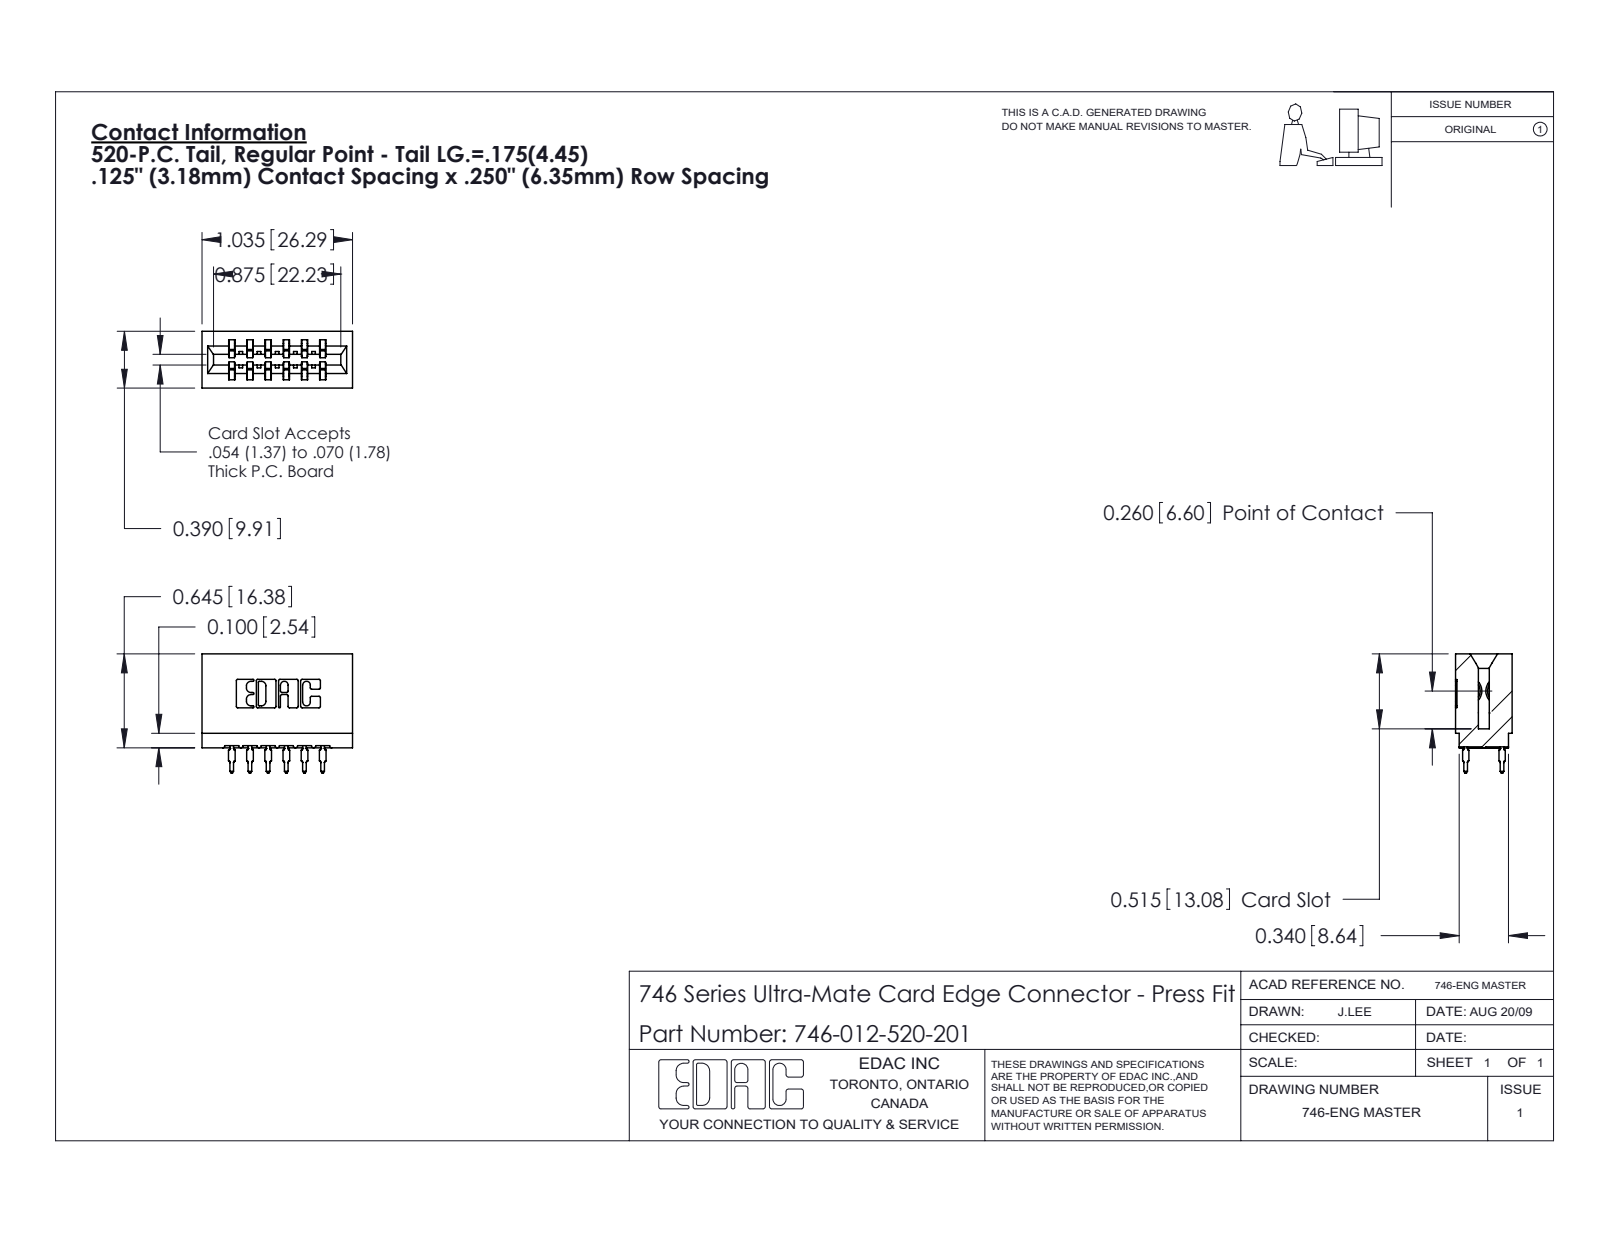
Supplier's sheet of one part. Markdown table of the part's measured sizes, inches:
| quantity | value |
| --- | --- |
| part name | 746-012-520-201; 746-292-001_520; 746 Part_.515 Slot Depth - 01 |
| STEP written by | SolidWorks 2020 (CONFIG_CONTROL_DESIGN) |
| units | inches |
| bodies | 13 solids, 1171 faces (607 planar, 252 cylindrical, 312 other) |
| overall size | 1.035 × 0.819 × 0.39 |
| volume | 0.185 in³ |
| surface area | 6.361 in² |
| partial cylindrical surfaces (radius × count) | 0.021 × 24, 0.01 × 22, 0.005 × 8, 0.011 × 8, 0.015 × 7, 0.007 × 6, 0.031 × 6, 0.026 × 3 |
| main face-to-face distances | 0.25, 0.125, 0.042, 0.057, 0.333, 0.125, 0.39, 0.292, 0.208, 0.375 |
